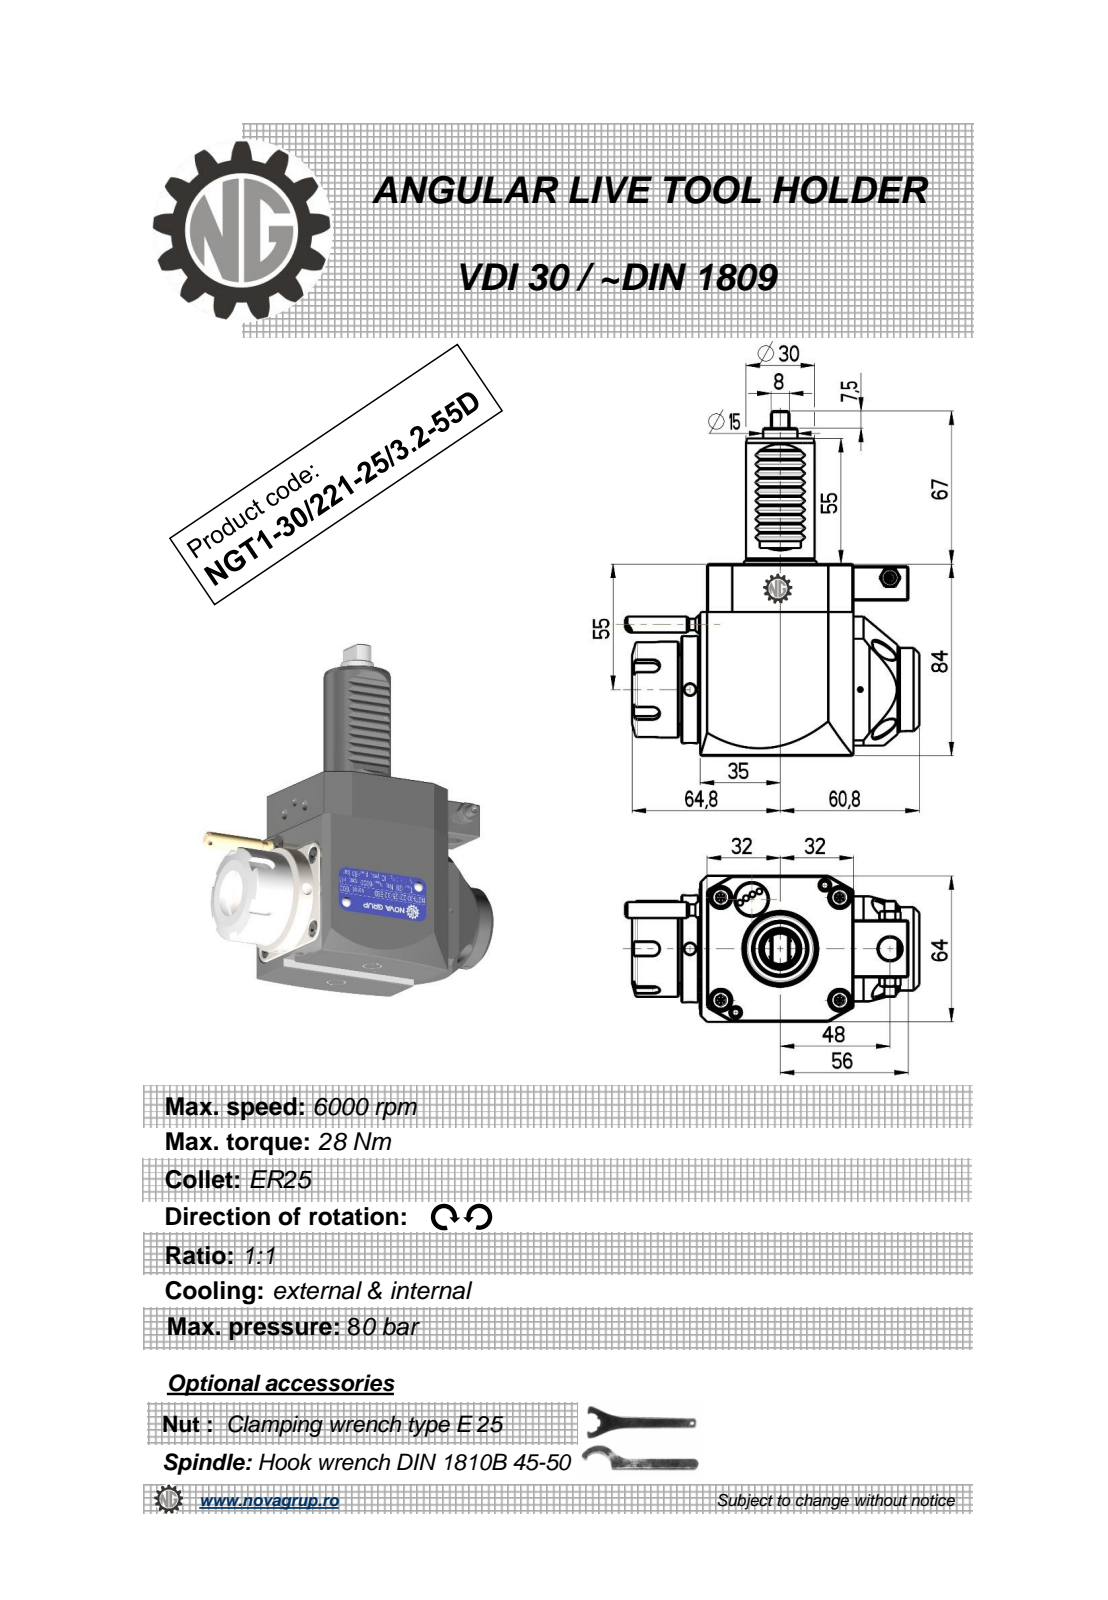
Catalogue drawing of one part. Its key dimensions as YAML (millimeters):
part_name: "NGT1_30_221_25_3_2_55D"
step_written_by: "PRO/ENGINEER BY PARAMETRIC TECHNOLOGY CORPORATION, 2010280 (CONFIG_CONTROL_DESIGN)"
units: millimeters
bodies: {solids: 1, faces: 429, planar: 195, cylindrical: 86, other: 148}
overall_size: [151, 128.63, 64]
volume: 479276
surface_area: 49439
round_holes:
  - {diameter: 5, count: 2}
  - {diameter: 2.5, count: 1}
  - {diameter: 3, count: 1}
  - {diameter: 4.2, count: 1}
  - {diameter: 9.5, count: 1}
  - {diameter: 10, count: 1}
  - {diameter: 20.3, count: 1}
round_bosses_or_shafts:
  - {diameter: 8.96, count: 2}
  - {diameter: 5, count: 2}
  - {diameter: 47, count: 1}
  - {diameter: 42, count: 1}
  - {diameter: 36.5, count: 1}
  - {diameter: 35, count: 1}
  - {diameter: 30, count: 1}
  - {diameter: 15, count: 1}
partial_cylinders:
  - {radius: 0.26, count: 12}
  - {radius: 0.3, count: 10}
  - {radius: 3, count: 5}
  - {radius: 0.8, count: 2}
  - {radius: 160, count: 2}
  - {radius: 7.2, count: 1}
  - {radius: 32, count: 1}
face_to_face_distances: [64, 84, 0.5, 67.2, 7.5, 67, 3.2, 3, 55, 8]
hole_center_spacings: [24.76, 33.19, 46.5, 87.45, 100.24]
